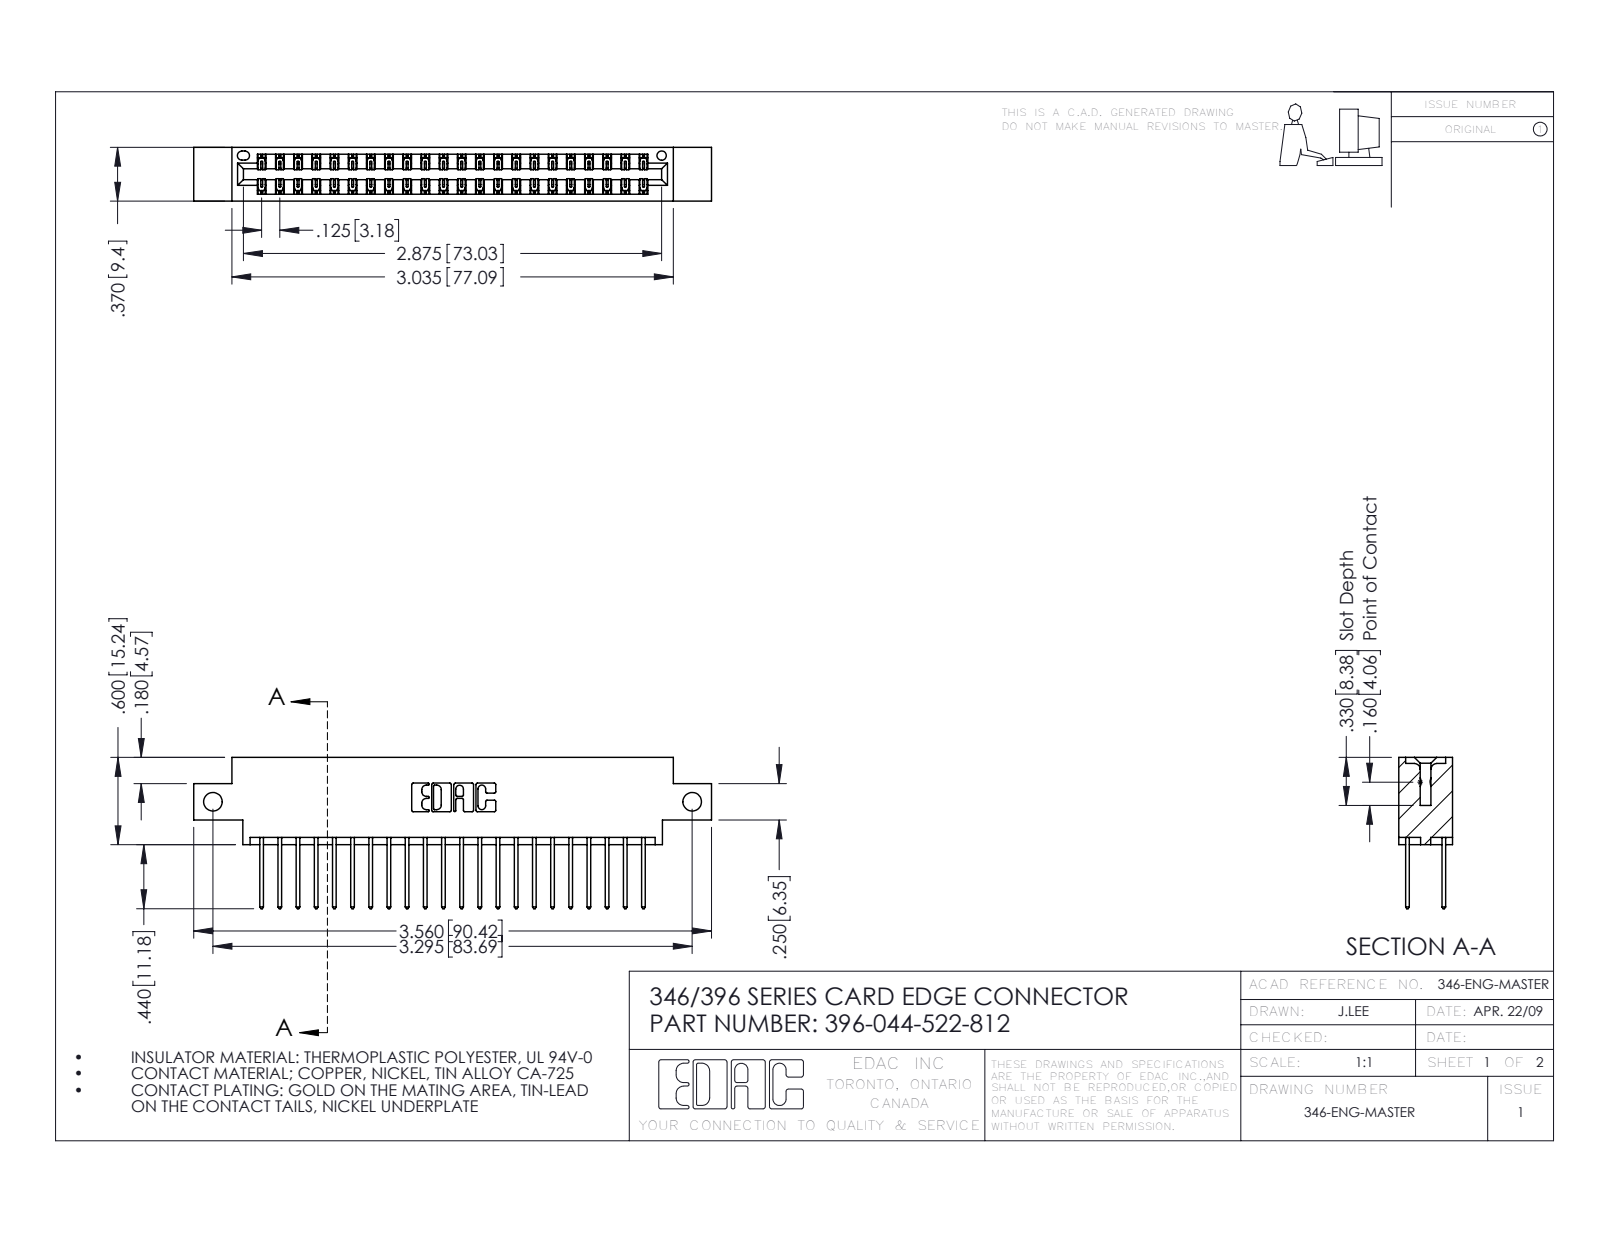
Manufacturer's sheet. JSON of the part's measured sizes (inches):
{"part_name": "396-044-522-812; 345-292-001_345-293-122; 346 Part_0.170 Offset - Side Mount", "step_written_by": "SolidWorks 2016 (CONFIG_CONTROL_DESIGN)", "units": "inches", "bodies": {"solids": 45, "faces": 2414, "planar": 1620, "cylindrical": 794, "other": 0}, "overall_size": [3.56, 1.04, 0.37], "volume_in3": 0.521, "surface_area_in2": 18.57, "round_holes": [[0.128, 2], [0.064, 1]], "partial_cylinders_radius": [[0.006, 66], [0.01, 44], [0.01, 22], [0.007, 6], [0.031, 6], [0.026, 3], [0.014, 2], [0.022, 2]], "face_to_face_distances": [0.048, 0.322, 0.25, 0.37, 0.072, 0.298, 0.025, 0.275, 0.148, 0.222], "hole_center_spacings": [3.295]}
